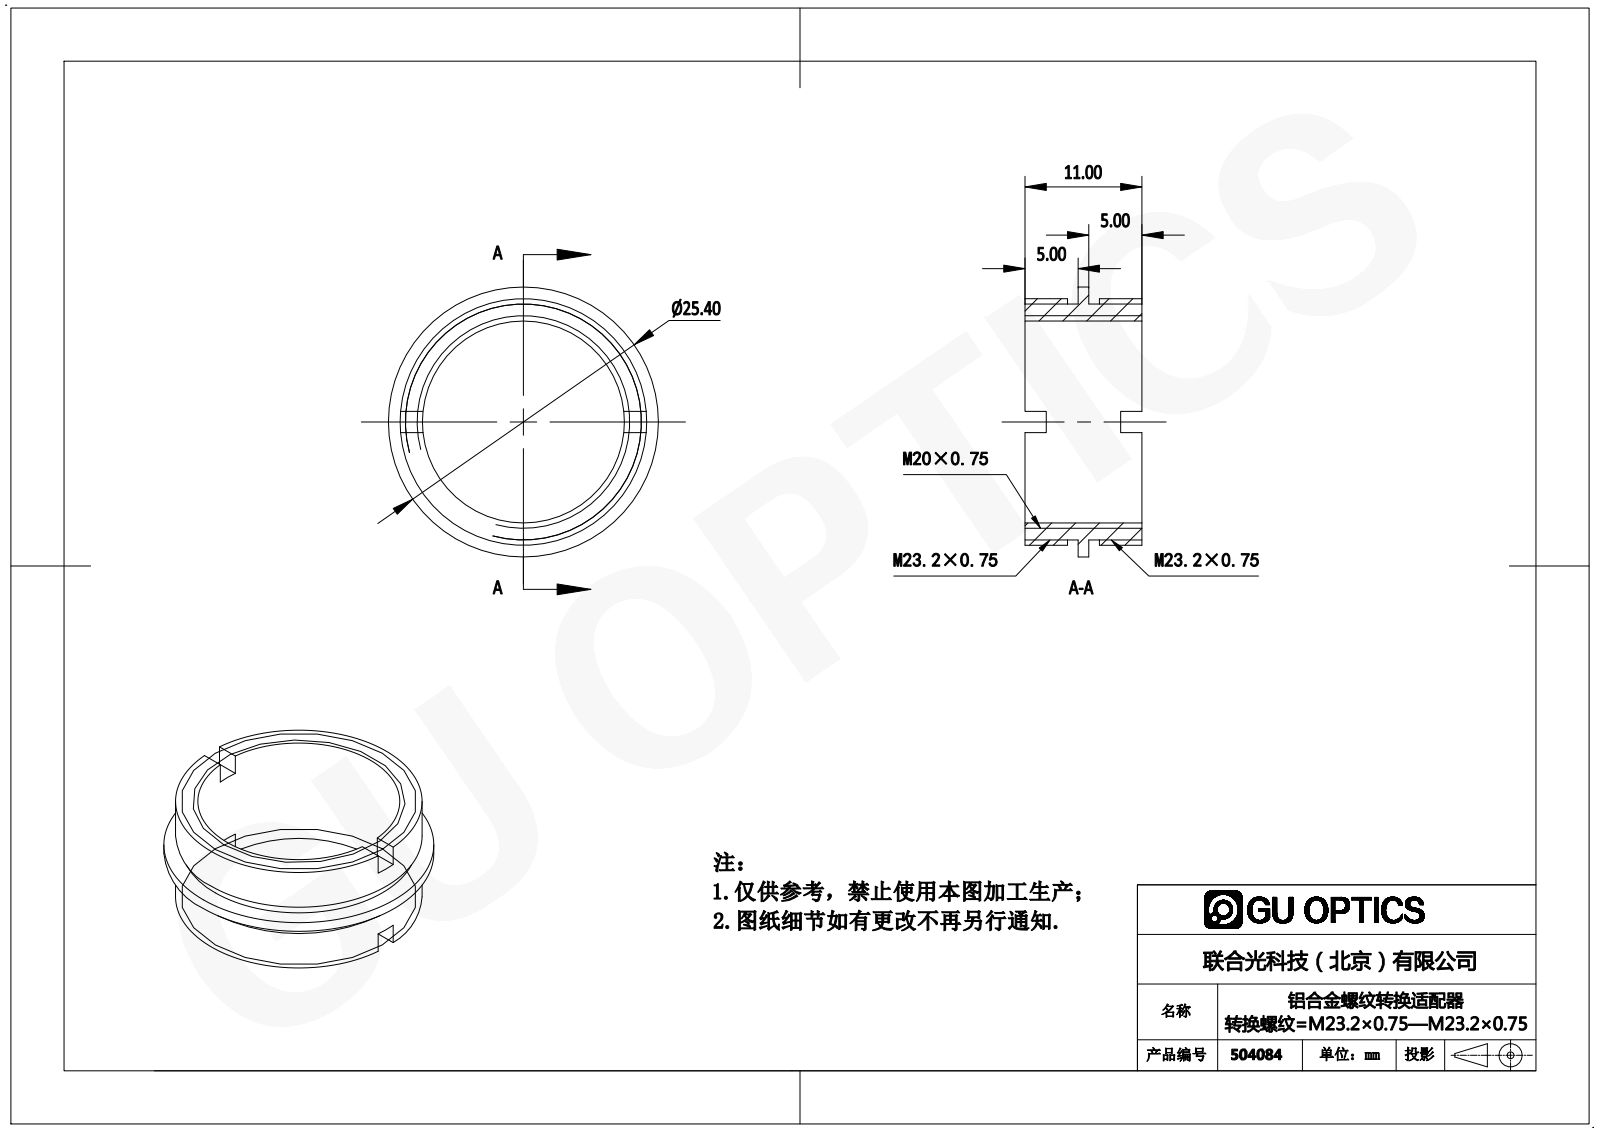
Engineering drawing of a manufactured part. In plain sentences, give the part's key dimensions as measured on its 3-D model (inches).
The part is named "504084". Its 3-D file was written by "SolidWorks 2016 (AUTOMOTIVE_DESIGN)". It is 1 solid with 32 faces: 20 planar, 12 cylindrical and 0 other. Overall it measures 1 by 1 by 0.433 inches. Its volume is 0.092 cubic inches and its surface area 3.178 square inches. Round holes: 1 of diameter 0.748. Round bosses or shafts: 1 of diameter 1, 1 of diameter 0.913, 1 of diameter 0.874. The main face-to-face distances are 0.197, 0.236, 0.039, 0.433, 0.079, 0.157, 0.276, 0.118, 0.354.
